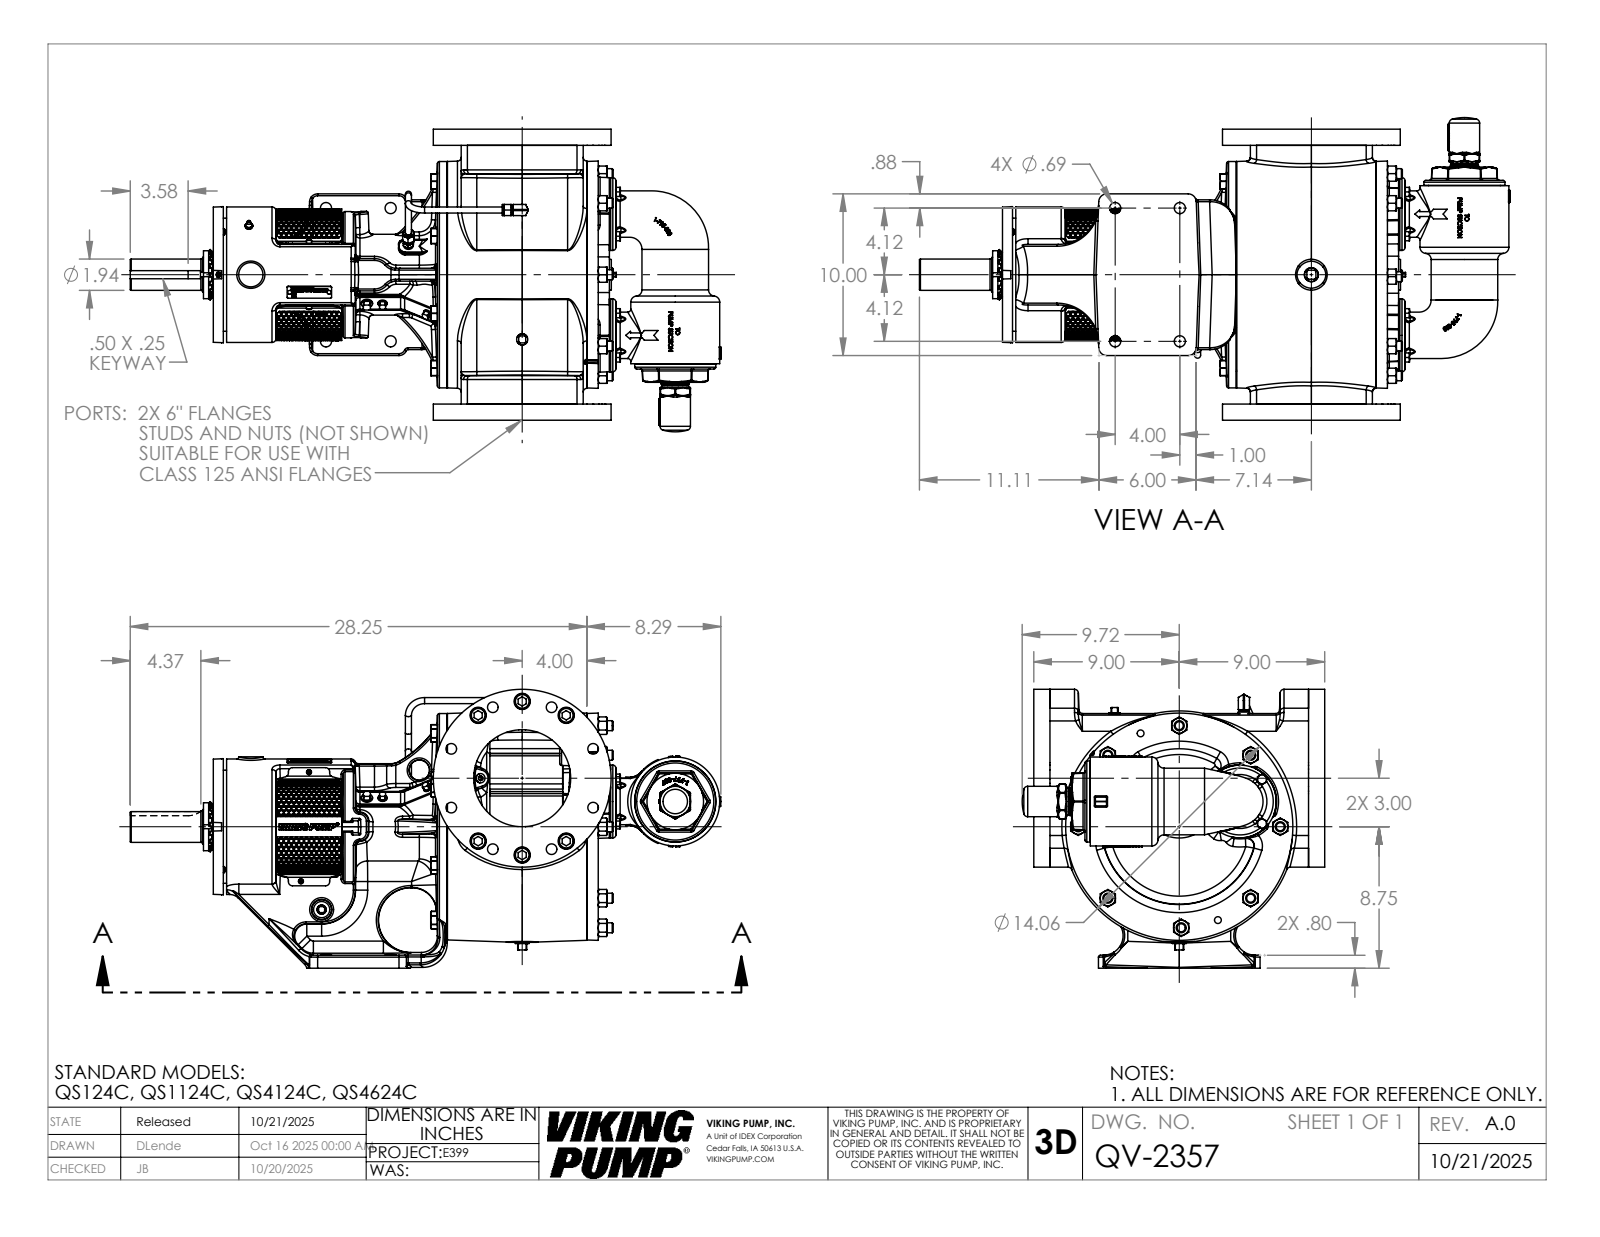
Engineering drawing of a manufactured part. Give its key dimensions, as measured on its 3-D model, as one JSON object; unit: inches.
{"part_name": "QV-2357", "step_written_by": "SolidWorks 2024 (AUTOMOTIVE_DESIGN)", "units": "inches", "bodies": {"solids": 1, "faces": 4918, "planar": 1632, "cylindrical": 811, "other": 2475}, "overall_size": [36.542, 18.719, 17.25], "volume_in3": 2776, "surface_area_in2": 2587, "round_holes": [[0.25, 9], [0.266, 8], [0.406, 8], [0.41, 8], [0.656, 8], [1.157, 8], [1, 6], [0.688, 4], [0.875, 4], [0.159, 2], [0.313, 2], [0.422, 2]], "round_bosses_or_shafts": [[0.375, 12], [0.617, 8], [0.937, 6], [0.312, 3], [0.19, 3], [4.5, 2], [0.687, 2], [0.563, 2]], "partial_cylinders_radius": [[0.12, 66], [0.25, 22], [0.06, 20], [0.015, 18], [0.092, 18], [0.07, 16], [0.75, 14], [0.03, 13]], "face_to_face_distances": [18, 1, 17, 0.57, 23.817, 3.82, 19.998, 0.882, 17.118, 16.984], "hole_center_spacings": [3.75, 2.079, 4.75, 5.783, 2.713, 3.133, 3.788, 5.423]}
